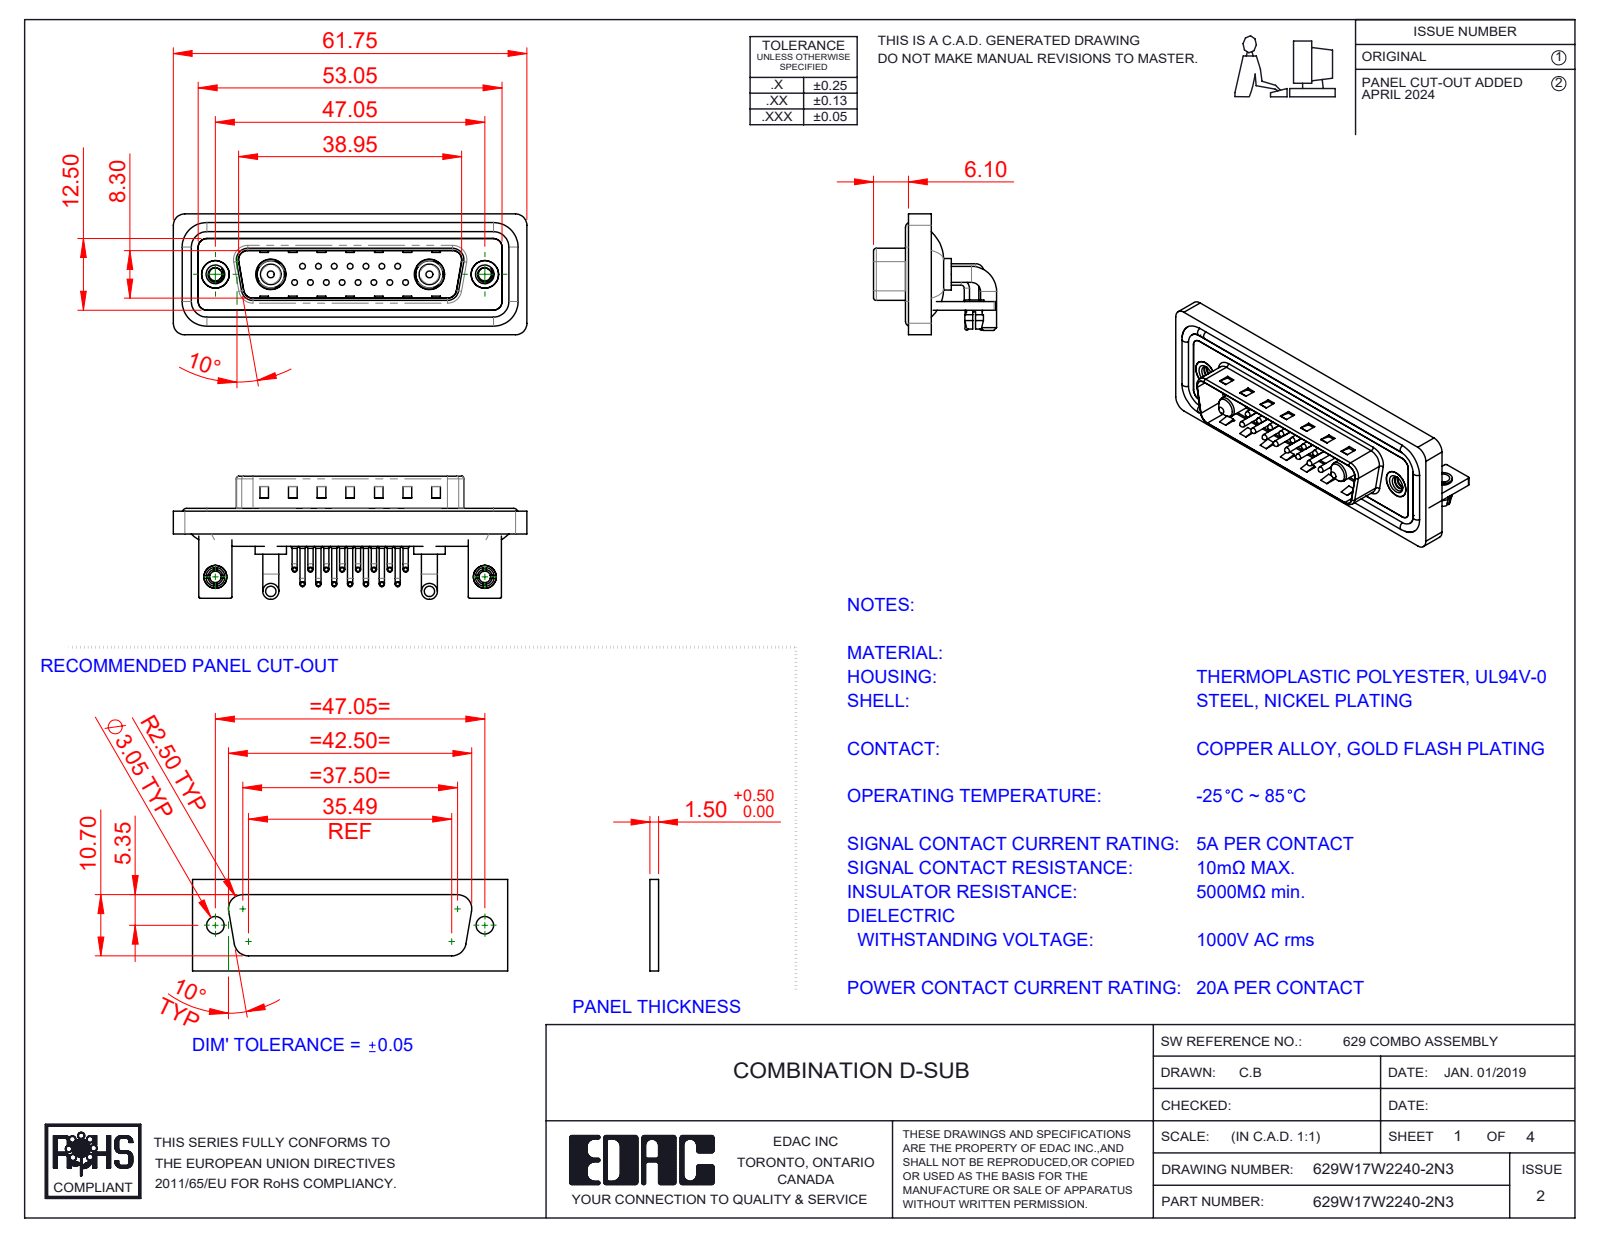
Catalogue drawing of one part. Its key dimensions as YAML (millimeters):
part_name: "629Combo Waterproof Housing_25 Contacts; Power Pin_20A RA; 629W17W2240-2N3; 629Combo Shell Front_25 Contacts (+7 more)"
step_written_by: "SolidWorks 2023 (CONFIG_CONTROL_DESIGN)"
units: millimeters
bodies: {solids: 30, faces: 2351, planar: 1257, cylindrical: 820, other: 274}
overall_size: [61.75, 21.5, 21.1]
volume: 7826
surface_area: 13398
round_holes:
  - {diameter: 2, count: 17}
  - {diameter: 0.75, count: 15}
  - {diameter: 1.6, count: 15}
  - {diameter: 2.26, count: 2}
  - {diameter: 2.5, count: 2}
  - {diameter: 3.2, count: 2}
  - {diameter: 4, count: 2}
  - {diameter: 4.8, count: 2}
  - {diameter: 4.85, count: 2}
  - {diameter: 5, count: 2}
  - {diameter: 5.3, count: 2}
round_bosses_or_shafts:
  - {diameter: 0.9, count: 30}
  - {diameter: 1.5, count: 15}
  - {diameter: 1, count: 15}
  - {diameter: 0.65, count: 15}
  - {diameter: 2.8, count: 4}
  - {diameter: 1.6, count: 4}
  - {diameter: 5.5, count: 2}
  - {diameter: 5.2, count: 2}
partial_cylinders:
  - {radius: 2, count: 19}
  - {radius: 1.5, count: 18}
  - {radius: 0.25, count: 16}
  - {radius: 1.01, count: 15}
  - {radius: 0.5, count: 9}
  - {radius: 1.6, count: 8}
  - {radius: 0.6, count: 4}
  - {radius: 0.65, count: 4}
face_to_face_distances: [0.4, 0.8, 1.5, 2.1, 2.9, 1.1, 4.1, 1.6, 4.5, 3.7]
hole_center_spacings: [3.16, 2.77, 5.54, 8.31, 5.04, 7.49, 11.08, 5.03]
